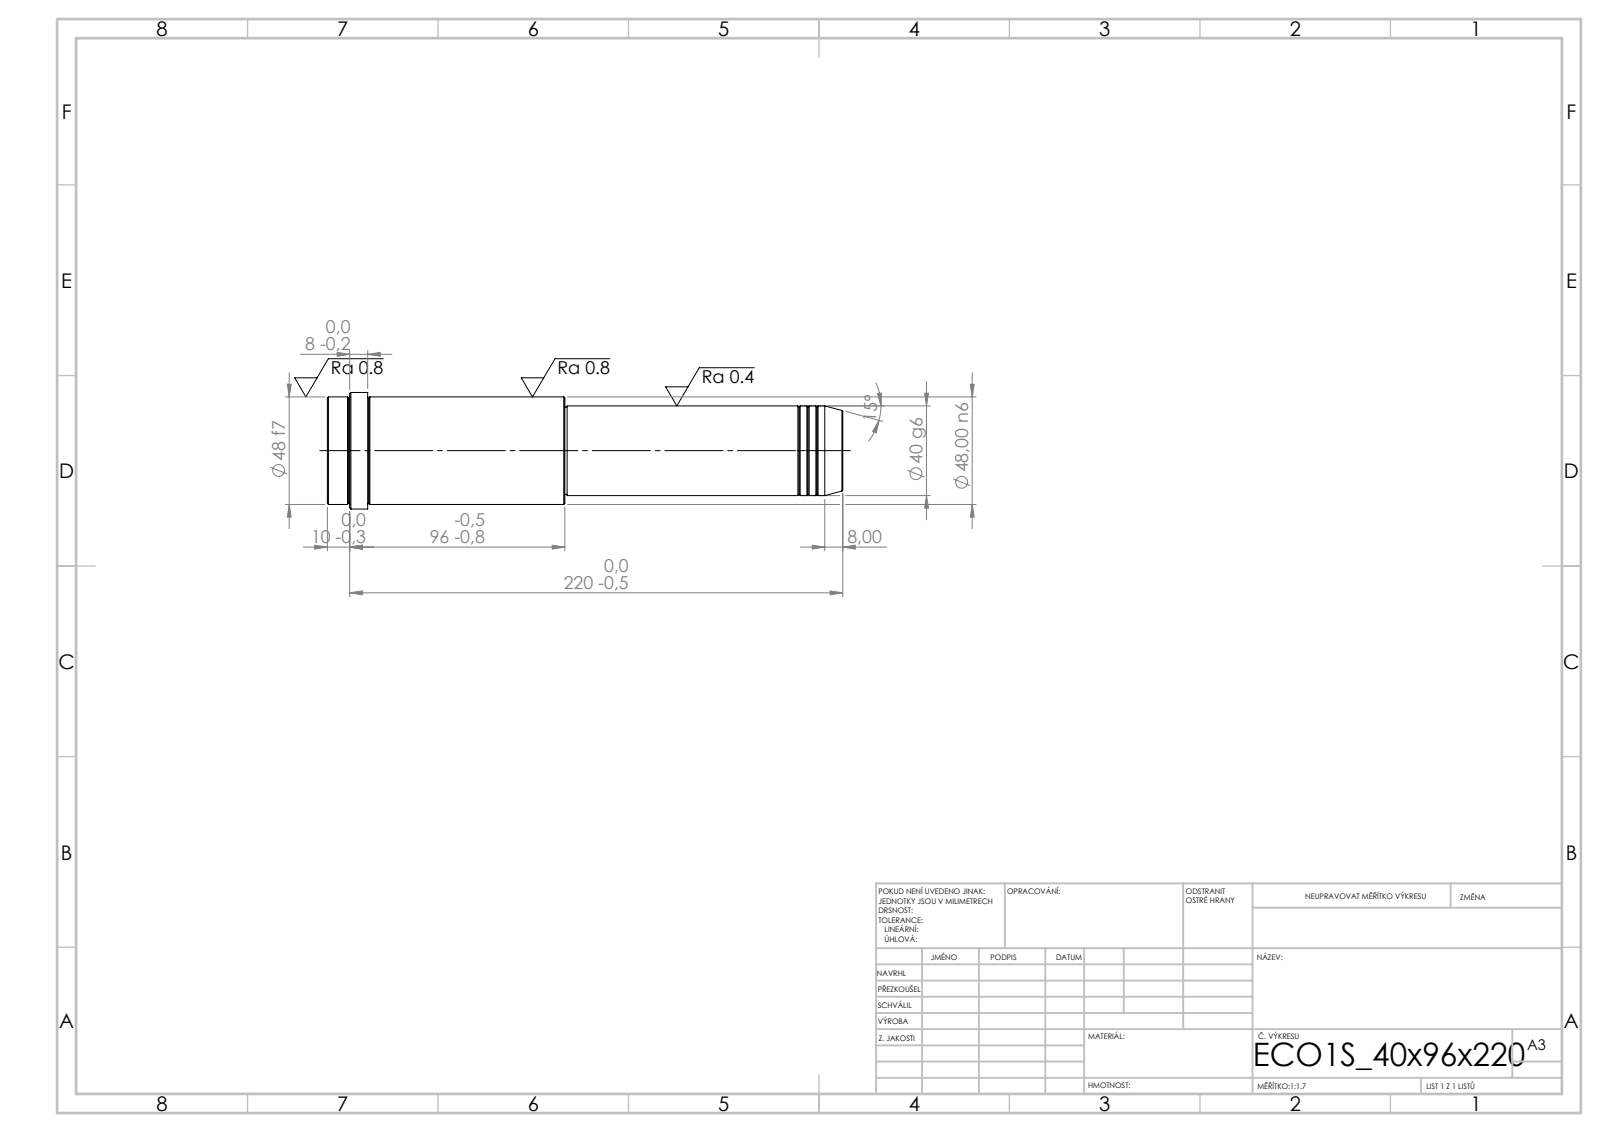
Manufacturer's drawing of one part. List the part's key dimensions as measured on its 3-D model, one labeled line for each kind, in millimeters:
STEP written by: SolidWorks 2019 (CONFIG_CONTROL_DESIGN)
Units: millimetres
Bodies: 1 solid, 52 faces (6 planar, 16 cylindrical, 30 other)
Overall size (bounding box): 230 × 52 × 52
Volume: 348 724 mm³ · Surface area: 35 982 mm²
Round bosses / shafts (diameter × count): ⌀52 ×1, ⌀48 ×1, ⌀40 ×1, ⌀39 ×1
Main face-to-face distances: 230, 124, 106, 212, 88, 18, 220, 96, 8, 10
